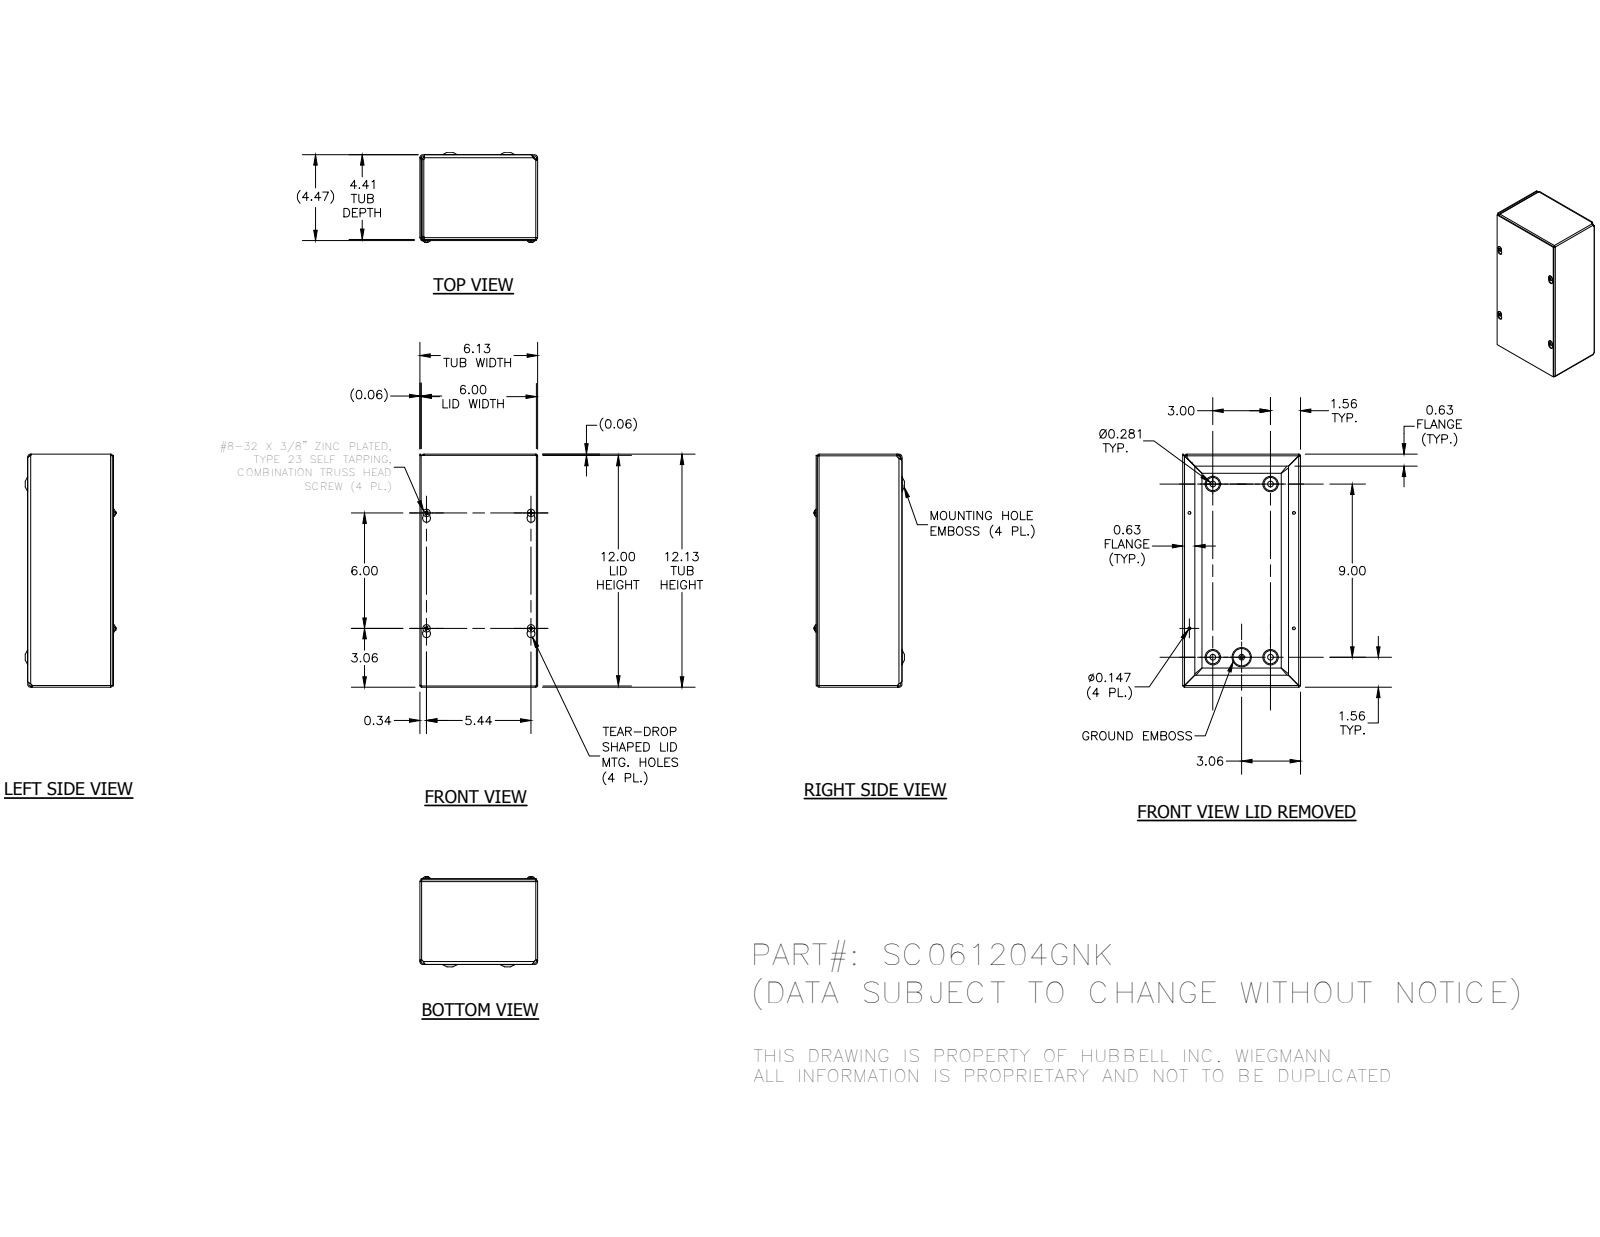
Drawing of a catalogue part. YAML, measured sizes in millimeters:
part_name: "SC0612GNKBKP; SC061204GNKWRA; SC0612GNKLID; 34056 (+1 more)"
step_written_by: "Autodesk Inventor 2014 (AUTOMOTIVE_DESIGN)"
units: millimeters
bodies: {solids: 7, faces: 358, planar: 133, cylindrical: 73, other: 152}
overall_size: [307.98, 155.57, 119.2]
volume: 351312
surface_area: 452865
round_holes:
  - {diameter: 3.73, count: 4}
  - {diameter: 7.62, count: 4}
  - {diameter: 4.19, count: 1}
round_bosses_or_shafts:
  - {diameter: 9.75, count: 4}
  - {diameter: 4.17, count: 4}
  - {diameter: 5.8, count: 1}
partial_cylinders:
  - {radius: 0.79, count: 8}
  - {radius: 2.37, count: 8}
  - {radius: 1.4, count: 4}
  - {radius: 1.57, count: 4}
  - {radius: 2.38, count: 4}
  - {radius: 2.97, count: 4}
  - {radius: 3.15, count: 4}
  - {radius: 3.17, count: 4}
face_to_face_distances: [1.57, 110.32, 111.89, 1.58, 1.59, 111.91, 113.48, 155.58, 154.01, 154]
hole_center_spacings: [38.1, 76.2, 113.72, 138.11, 152.4, 192.98, 193.02, 202.61]
